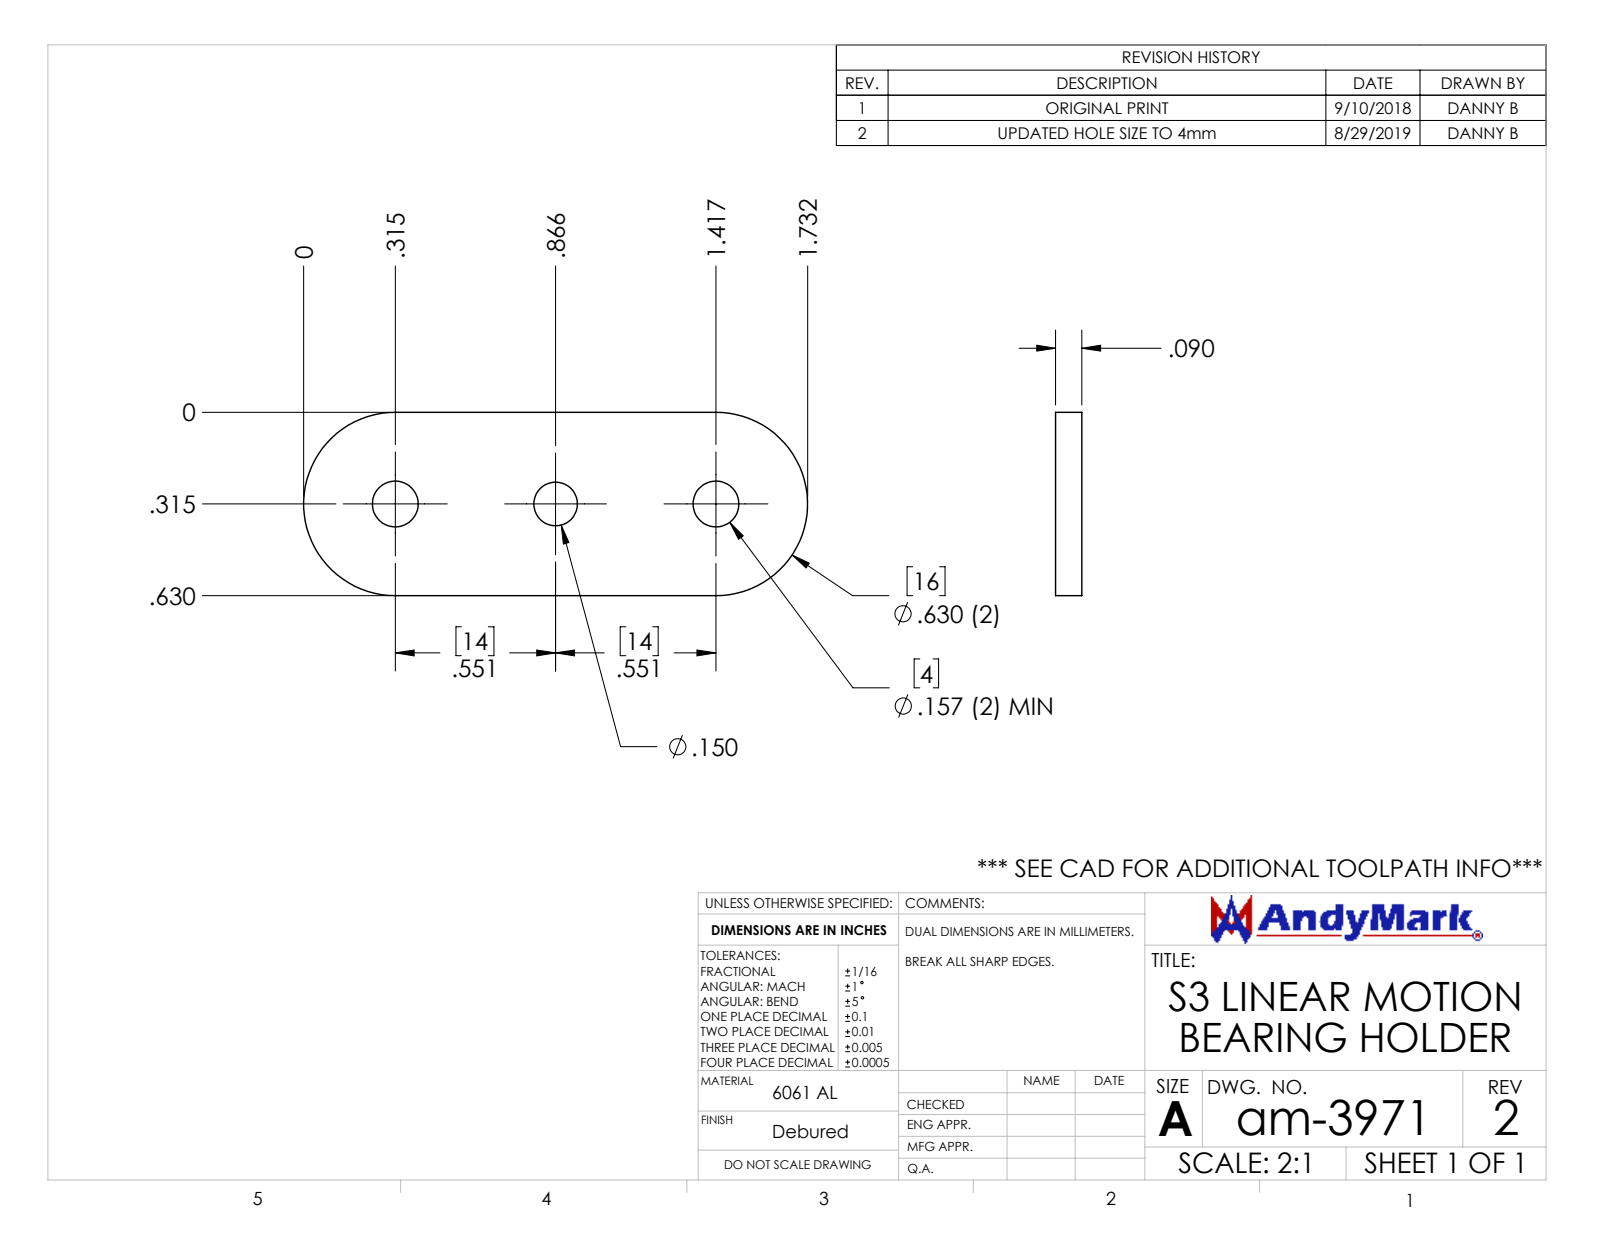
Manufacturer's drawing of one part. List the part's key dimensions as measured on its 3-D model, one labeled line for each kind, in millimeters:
Part name (STEP PRODUCT): am-3971 S3 Linear Motion Bearing Holder
STEP written by: SolidWorks 2019 (AUTOMOTIVE_DESIGN)
Units: millimetres
Bodies: 1 solid, 13 faces (4 planar, 9 cylindrical, 0 other)
Overall size (bounding box): 44 × 16 × 2.3
Volume: 1 400 mm³ · Surface area: 1 553 mm²
Round holes (diameter × count): ⌀4 ×2, ⌀3.8 ×1
Partial cylindrical surfaces — rounded edges, fillets, slot ends (radius × count): R8 ×2
Main face-to-face distances: 2.3, 16
Hole centre spacings: 14, 28
